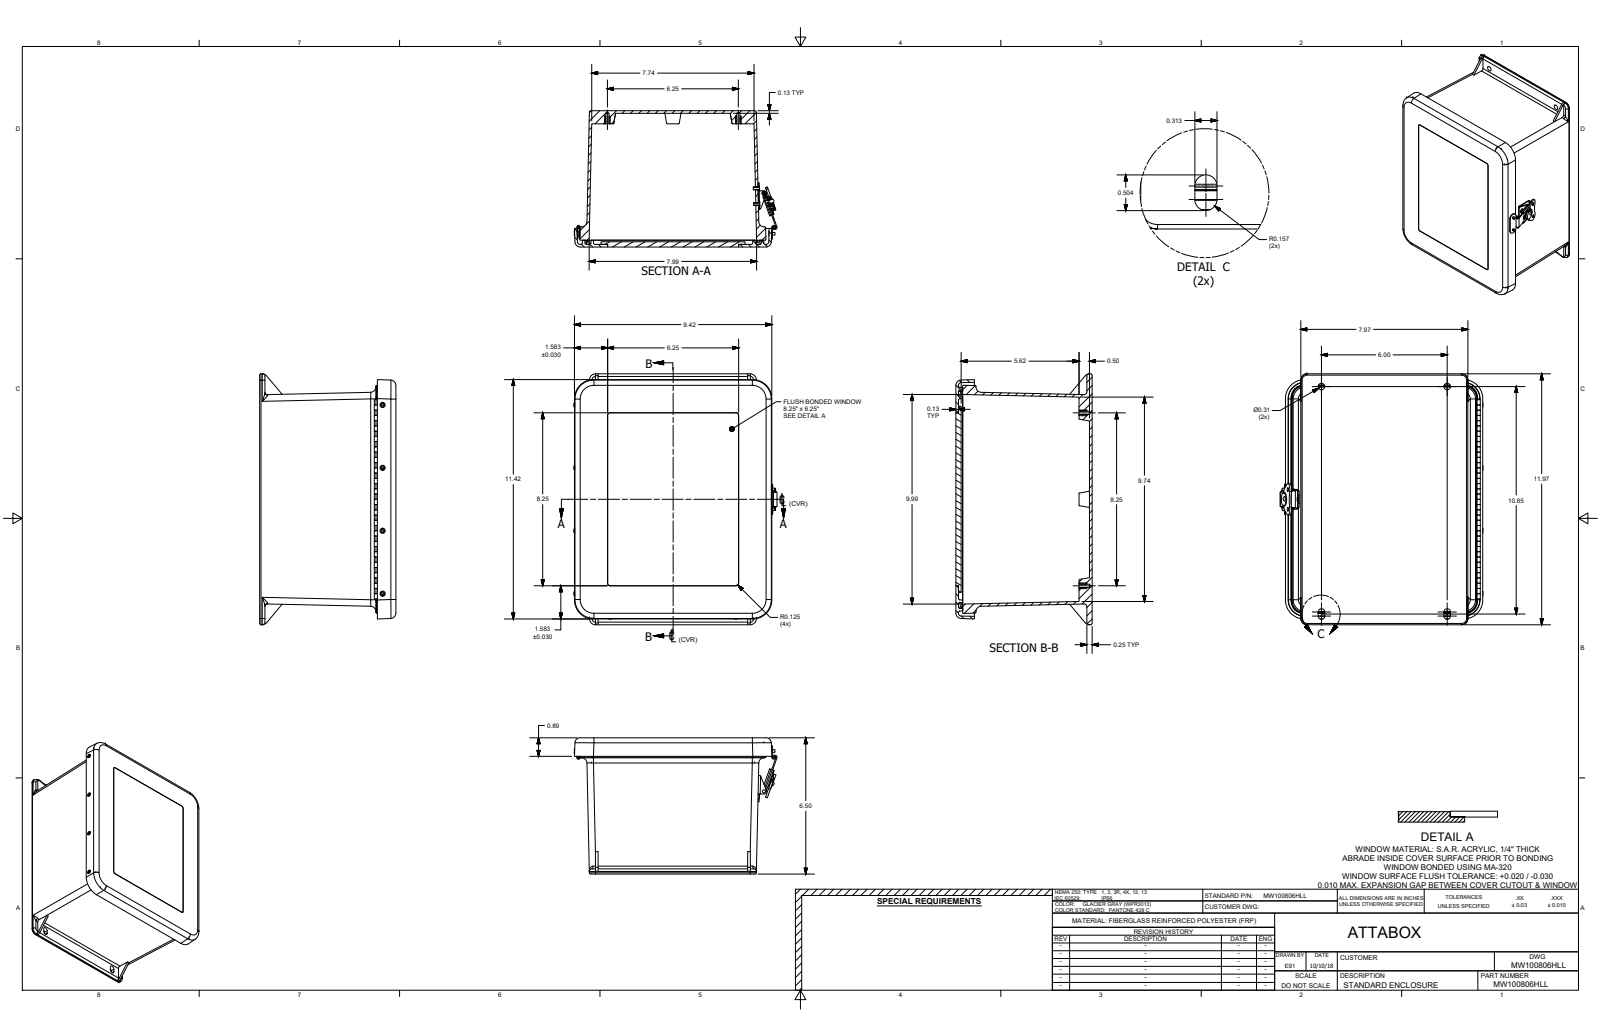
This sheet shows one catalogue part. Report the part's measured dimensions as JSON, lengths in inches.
{"part_name": "MW100806HLL", "step_written_by": "SolidWorks 2018 (AUTOMOTIVE_DESIGN)", "units": "inches", "bodies": {"solids": 41, "faces": 1216, "planar": 482, "cylindrical": 473, "other": 261}, "overall_size": [11.966, 9.676, 6.5], "volume_in3": 84.23, "surface_area_in2": 1059, "round_holes": [[0.14, 13], [0.104, 12], [0.152, 12], [0.159, 12], [0.131, 8], [0.13, 2], [0.133, 2], [0.187, 2], [0.313, 2], [0.375, 2], [0.375, 2], [0.067, 1]], "round_bosses_or_shafts": [[0.27, 12], [0.125, 7], [0.125, 6], [0.66, 1], [0.582, 1], [0.525, 1], [0.286, 1], [0.213, 1]], "partial_cylinders_radius": [[0.031, 26], [0.125, 23], [0.062, 21], [0.063, 20], [0.039, 16], [0.063, 13], [0.3, 12], [0.25, 11]], "face_to_face_distances": [0.122, 0.125, 6.375, 6.5, 6.25, 0.25, 6.125, 0.125, 6.25, 0.203], "hole_center_spacings": [6, 3, 2.5, 3.5, 8.5, 0.013, 9, 0.125]}
